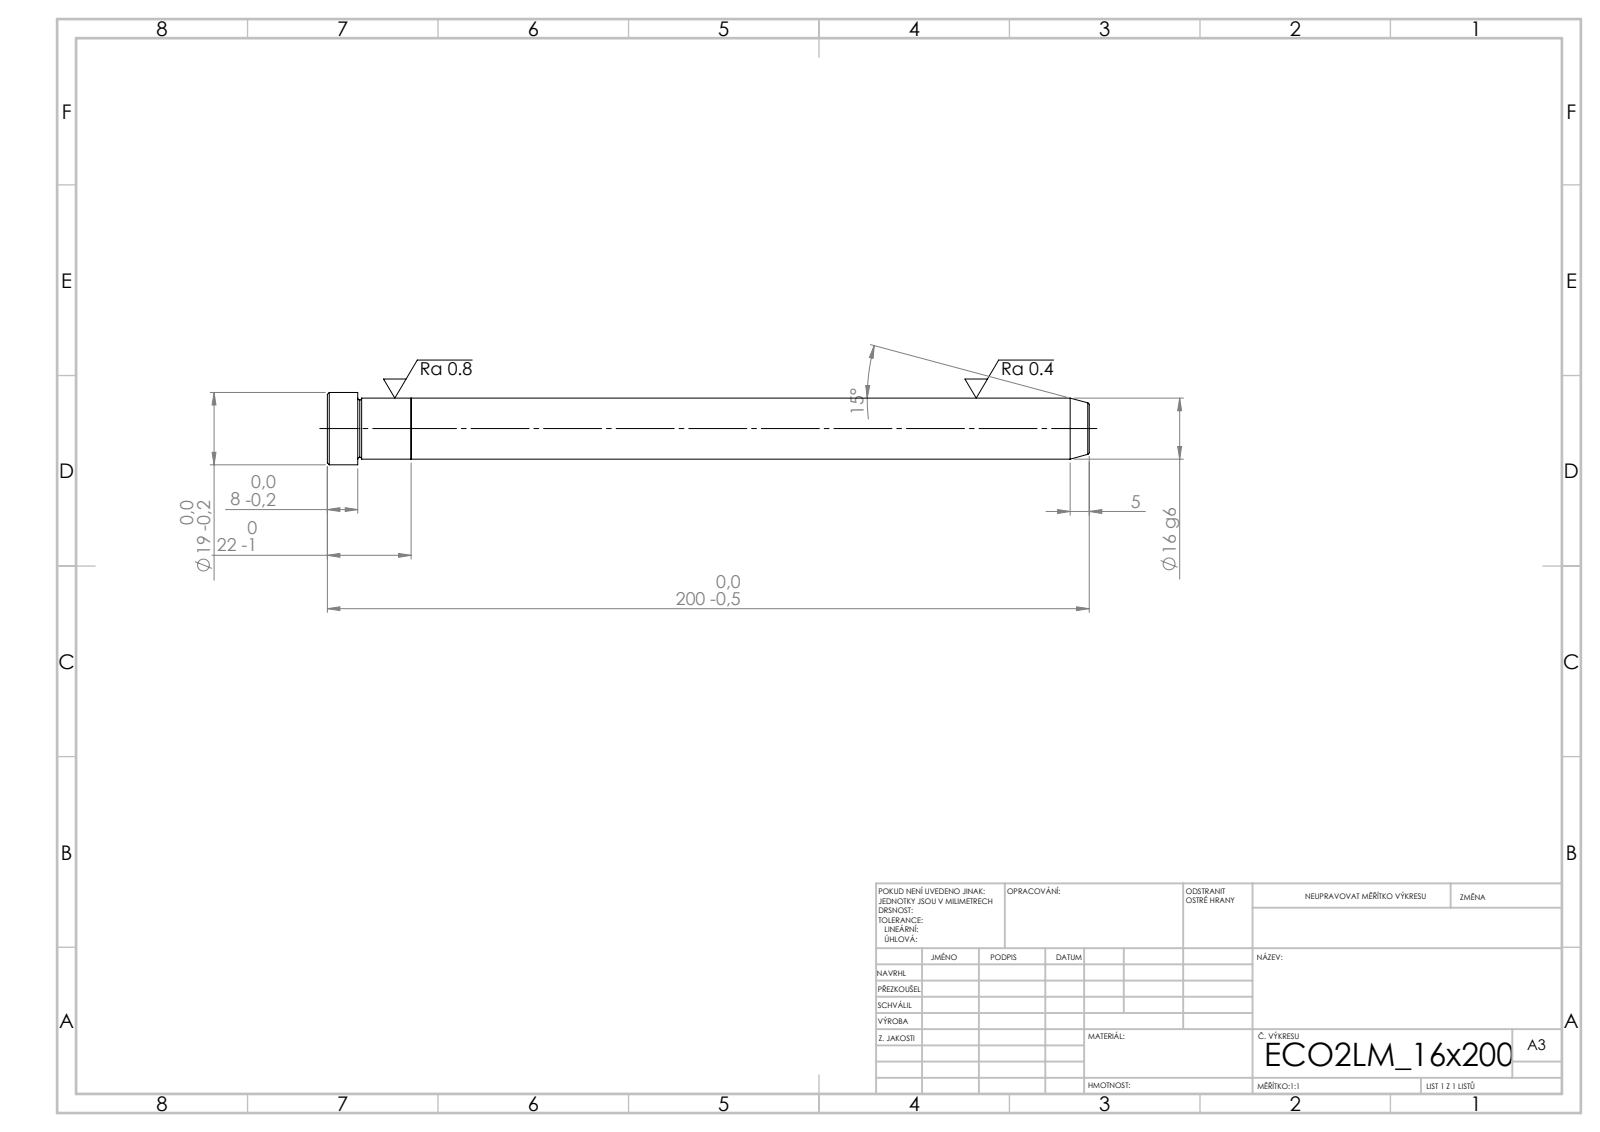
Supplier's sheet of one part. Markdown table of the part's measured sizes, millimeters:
| quantity | value |
| --- | --- |
| STEP written by | SolidWorks 2019 (CONFIG_CONTROL_DESIGN) |
| units | millimeters |
| bodies | 2 solids, 21 faces (5 planar, 6 cylindrical, 10 other) |
| overall size | 200 × 19 × 19 |
| volume | 40 685 mm³ |
| surface area | 11 026 mm² |
| round bosses / shafts (diameter × count) | 19 × 1, 16 × 1 |
| main face-to-face distances | 22, 178, 200, 192, 14, 8 |
